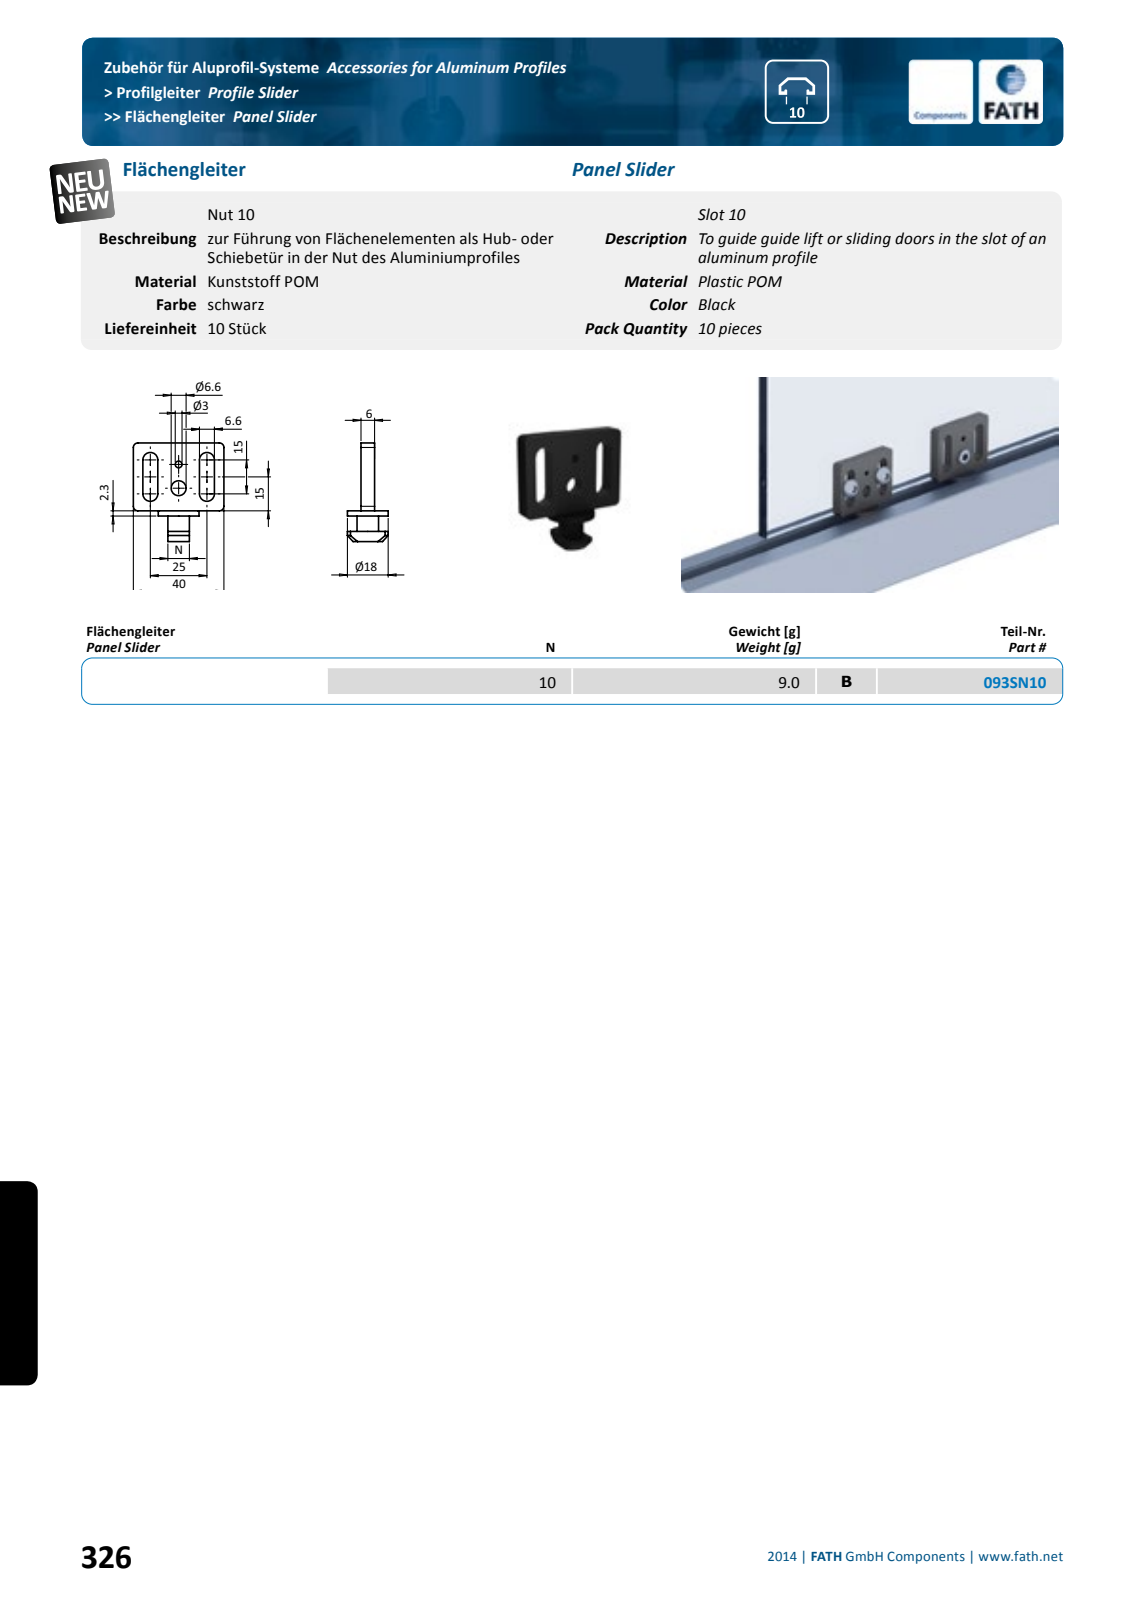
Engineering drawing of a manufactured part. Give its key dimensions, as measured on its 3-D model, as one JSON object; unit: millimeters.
{"part_name": "fath_093sn10", "step_written_by": "Spatial InterOp 3D (automotive_design)", "units": "millimeters", "bodies": {"solids": 1, "faces": 43, "planar": 19, "cylindrical": 20, "other": 4}, "overall_size": [43.6, 40, 18], "volume_mm3": 7064, "surface_area_mm2": 4382, "round_holes": [[3, 1], [6.6, 1]], "round_bosses_or_shafts": [[18, 1], [9.5, 1]], "partial_cylinders_radius": [[2, 4], [3.3, 4]], "face_to_face_distances": [6, 30, 32.3, 2.3, 10.8, 29.2, 4.2, 35.8, 6.6, 25], "hole_center_spacings": [10.5]}
